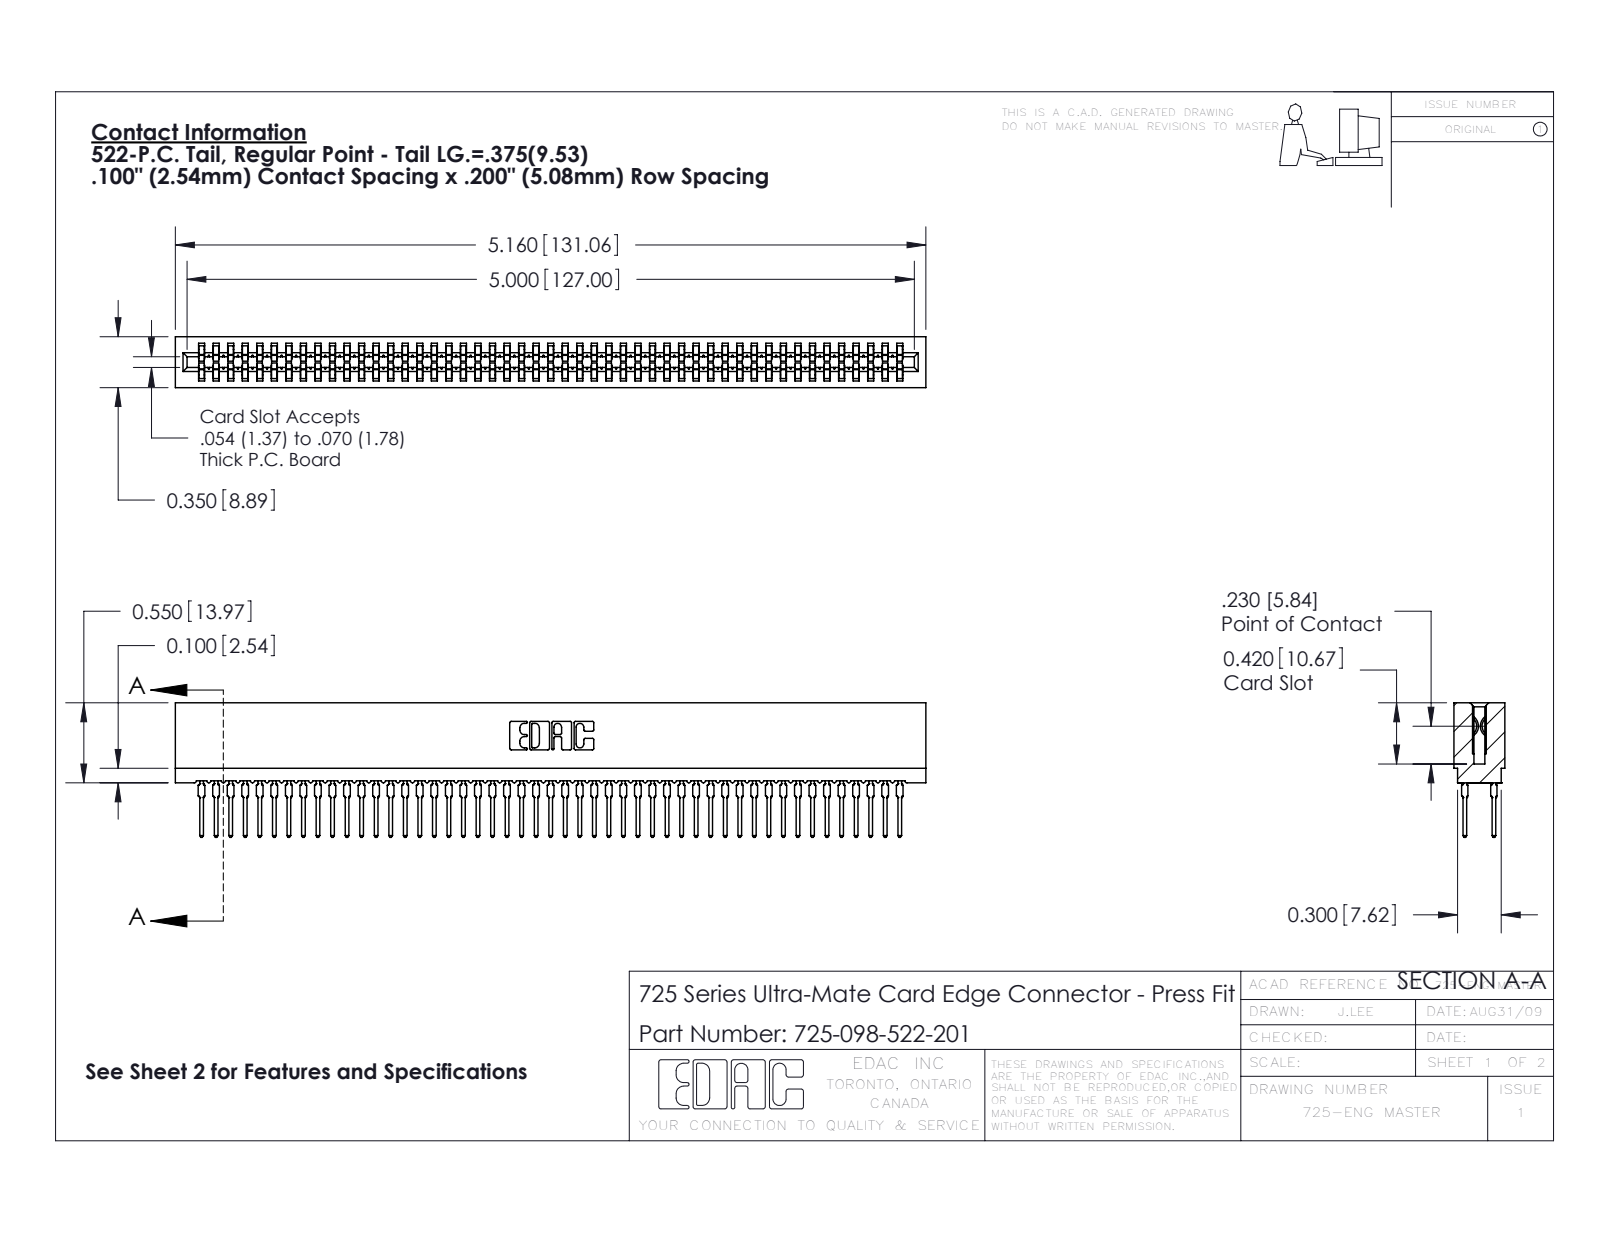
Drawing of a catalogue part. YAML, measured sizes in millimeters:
part_name: "725-098-522-201; 745-292-001_522; 725 Part_Insulator Option - 01"
step_written_by: "SolidWorks 2016 (CONFIG_CONTROL_DESIGN)"
units: millimeters
bodies: {solids: 99, faces: 8866, planar: 4563, cylindrical: 1755, other: 2548}
overall_size: [131.1, 23.5, 8.9]
volume: 10500
surface_area: 22610
partial_cylinders:
  - {radius: 0.5, count: 196}
  - {radius: 0.4, count: 98}
  - {radius: 0.3, count: 22}
  - {radius: 0.1, count: 8}
  - {radius: 0.3, count: 8}
  - {radius: 0.2, count: 6}
  - {radius: 0.8, count: 6}
  - {radius: 0.7, count: 3}
face_to_face_distances: [5.1, 1.6, 7.3, 8.9, 5.4, 3.5, 1.9, 3.8, 1.1, 7.7]
